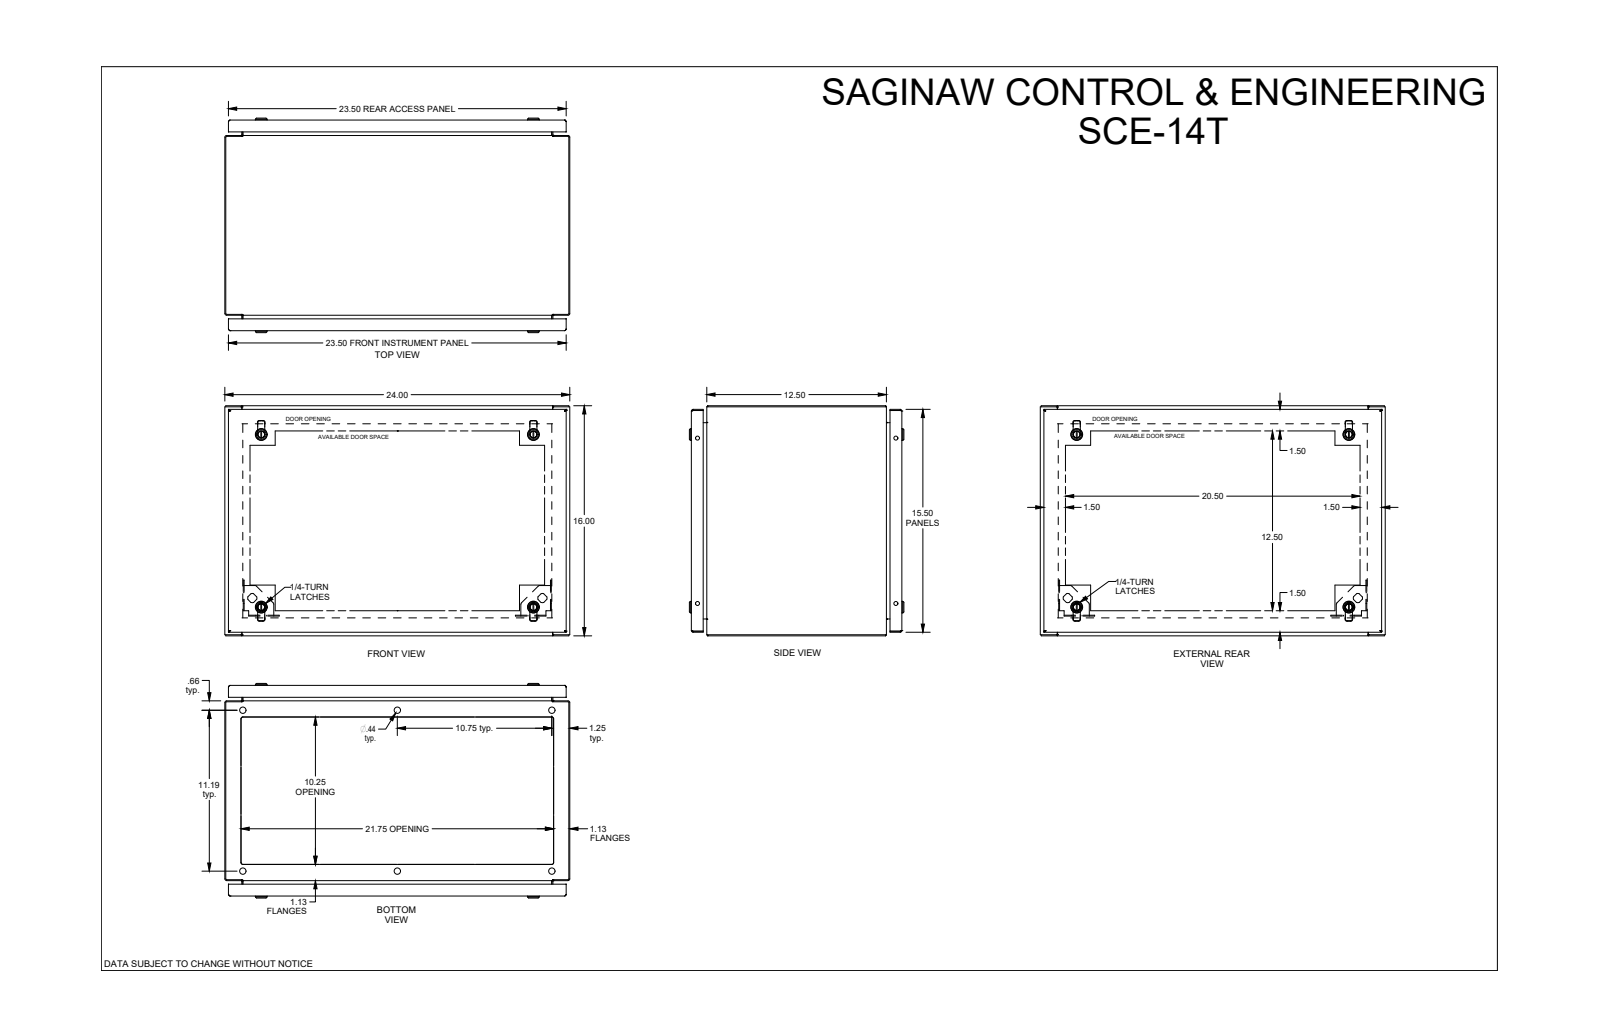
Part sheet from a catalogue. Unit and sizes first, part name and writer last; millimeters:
Units: millimetres
Overall size (bounding box): 609.6 × 406.4 × 379.1
Round holes (diameter × count): ⌀11.1 ×6, ⌀4.2 ×4, ⌀6 ×4, ⌀8.1 ×4, ⌀12 ×4, ⌀16.1 ×4
Round bosses / shafts (diameter × count): ⌀21 ×4, ⌀20 ×4, ⌀14 ×4, ⌀11.8 ×4, ⌀10.8 ×4, ⌀9.2 ×4, ⌀8 ×4, ⌀4.8 ×4
Partial cylindrical surfaces — rounded edges, fillets, slot ends (radius × count): R0.3 ×120, R0.5 ×62, R0.5 ×56, R3.2 ×26, R1.3 ×24, R2.6 ×16, R3.4 ×16, R4.3 ×16
Main face-to-face distances: 1.9, 1.5, 370.5, 607.7, 372.1, 369, 342.9, 27.3, 609.6, 605.8
Hole centre spacings: 273.1, 394.1, 284.2, 304.8, 481, 546.1, 569.4, 615.6
Volume: 2 463 000 mm³ · Surface area: 2 680 000 mm²
Bodies: 49 solids, 2898 faces (1424 planar, 1154 cylindrical, 320 other)
Part name (STEP PRODUCT): SCE-14T
STEP written by: SolidWorks 2019 (AUTOMOTIVE_DESIGN)
